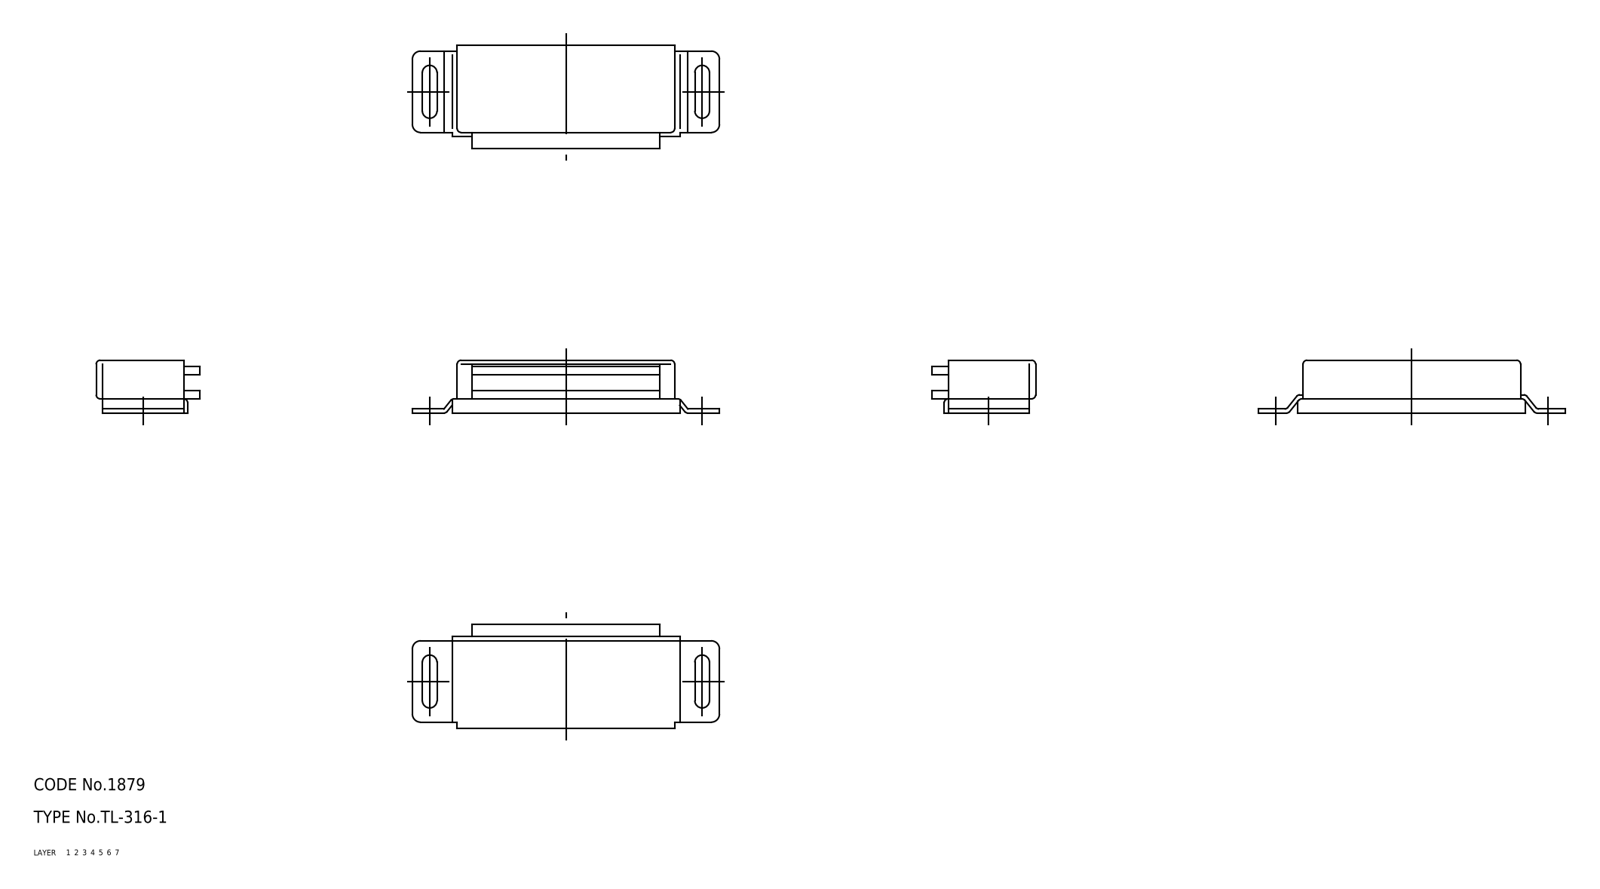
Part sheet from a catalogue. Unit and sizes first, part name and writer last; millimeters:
Units: millimetres
Overall size (bounding box): 75.5 × 25.5 × 13
Volume: 9 997 mm³ · Surface area: 13 903 mm²
Bodies: 4 solids, 91 faces (0 planar, 0 cylindrical, 91 other)
Part name (STEP PRODUCT): attachment; magnet; housing; TL_316_1_20650_36
STEP written by: CADfix (AUTOMOTIVE_DESIGN)
